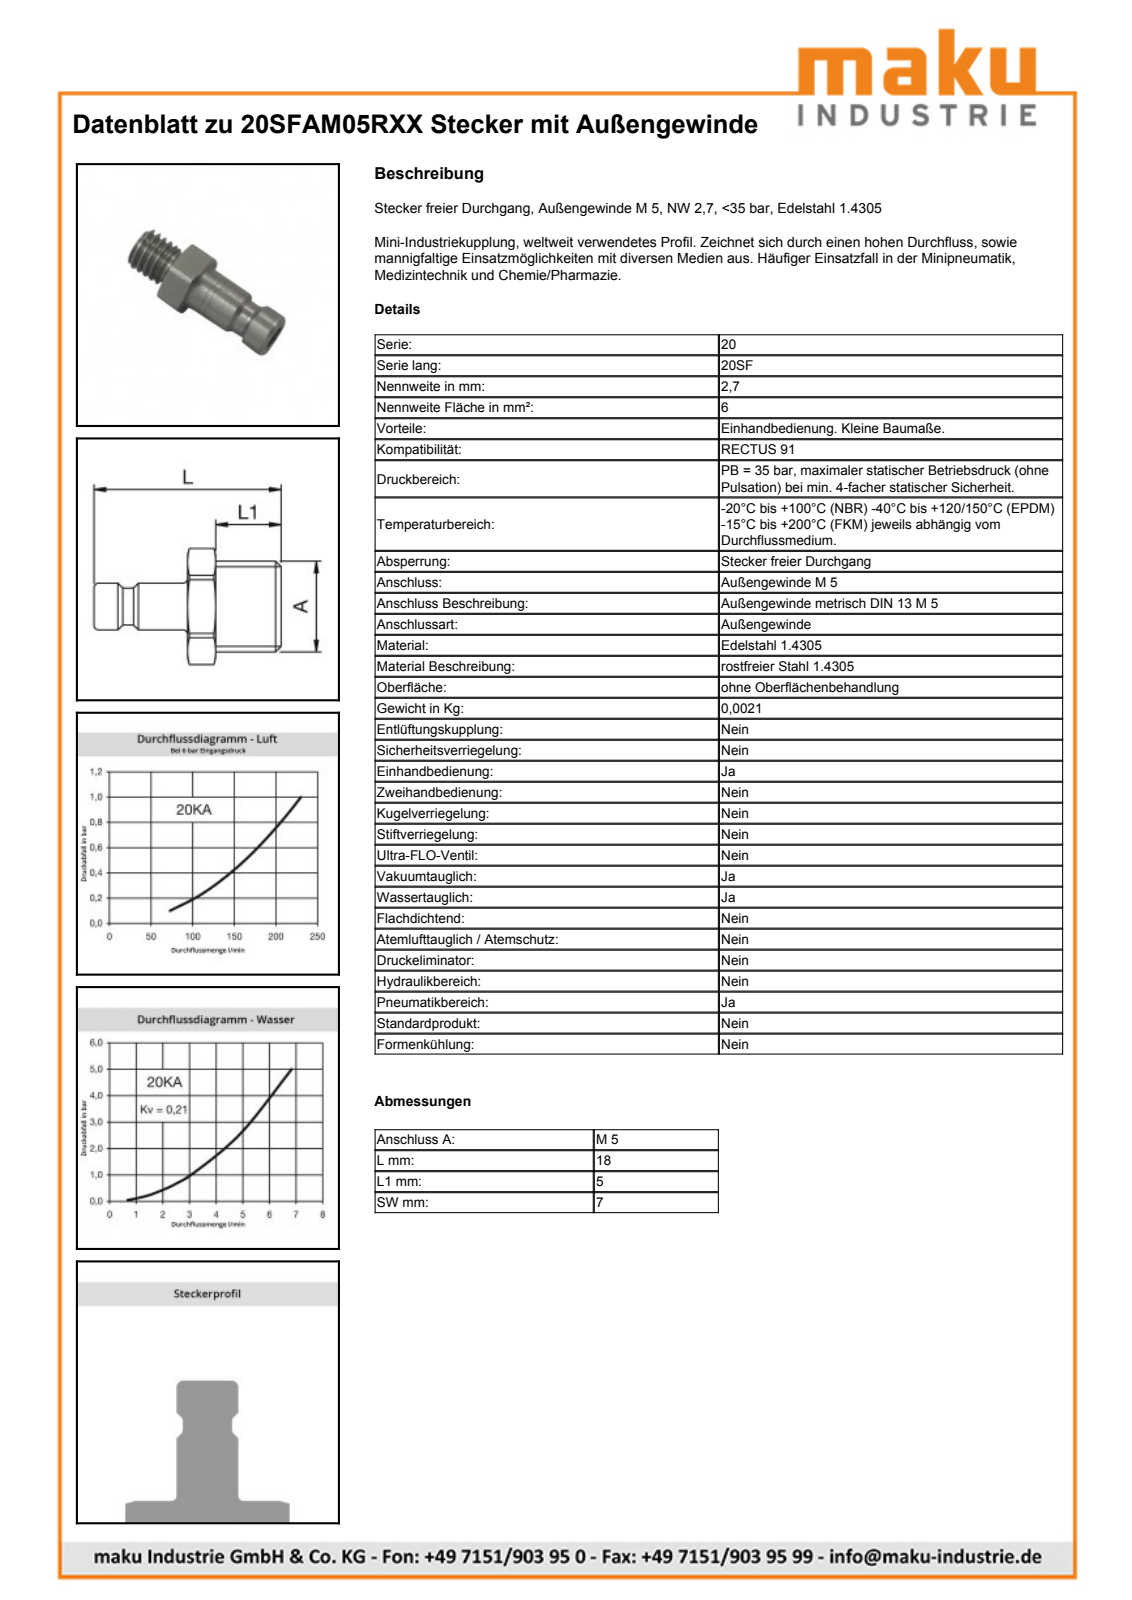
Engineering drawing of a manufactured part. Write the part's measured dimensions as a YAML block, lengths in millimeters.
part_name: "D107096"
step_written_by: "Autodesk Inventor 2013 (AUTOMOTIVE_DESIGN)"
units: millimeters
bodies: {solids: 1, faces: 43, planar: 10, cylindrical: 11, other: 22}
overall_size: [18, 7.9, 7]
volume: 299
surface_area: 525
round_holes:
  - {diameter: 2.7, count: 1}
round_bosses_or_shafts:
  - {diameter: 5, count: 1}
  - {diameter: 4, count: 1}
partial_cylinders:
  - {radius: 3.95, count: 1}
face_to_face_distances: [7, 3, 8, 5, 10, 13, 18]
